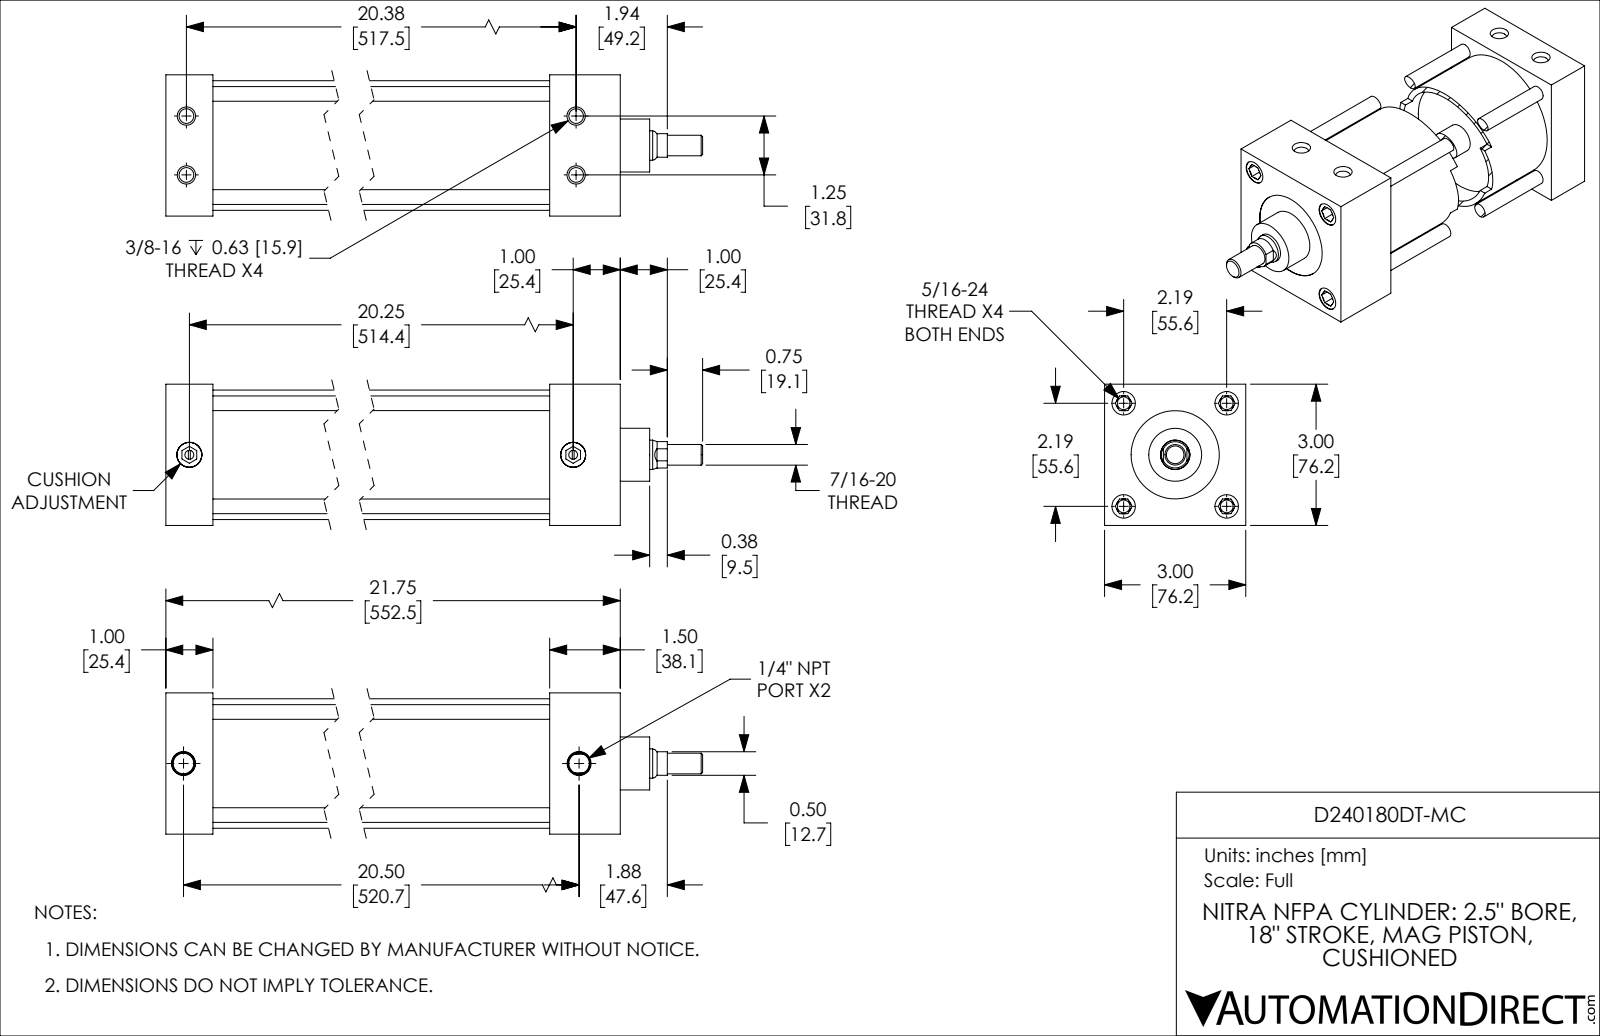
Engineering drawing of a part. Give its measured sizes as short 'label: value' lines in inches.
name: D240180DT-MC; D240180DT-MC_PISTON_KK1; D240180DT-MC_CUSHION; D240180DT-MC_BODY
written by: SolidWorks 2019 (CONFIG_CONTROL_DESIGN)
unit: in
bodies: 4 solids, 248 faces (90 planar, 78 cylindrical, 80 other)
size: 23.5 × 3 × 3
volume: 59.57 in³; area: 537.1 in²
holes: 4× ⌀0.272, 4× ⌀0.313, 4× ⌀0.5, 2× ⌀0.19, 2× ⌀0.438, 2× ⌀0.531, 1× ⌀0.626, 1× ⌀1.875, 1× ⌀2.501
bosses: 4× ⌀0.312, 2× ⌀0.532, 1× ⌀2.751, 1× ⌀2.499, 1× ⌀1.125, 1× ⌀0.624, 1× ⌀0.437
rounds: 1× R0.281
face distances: 3, 1, 20.25, 19.25, 21.75, 20.75, 1.5, 1.25, 2.25, 18
hole spacings: 1.548, 2.19, 0.628, 0.628, 1.25, 3.097, 20.375, 20.413
